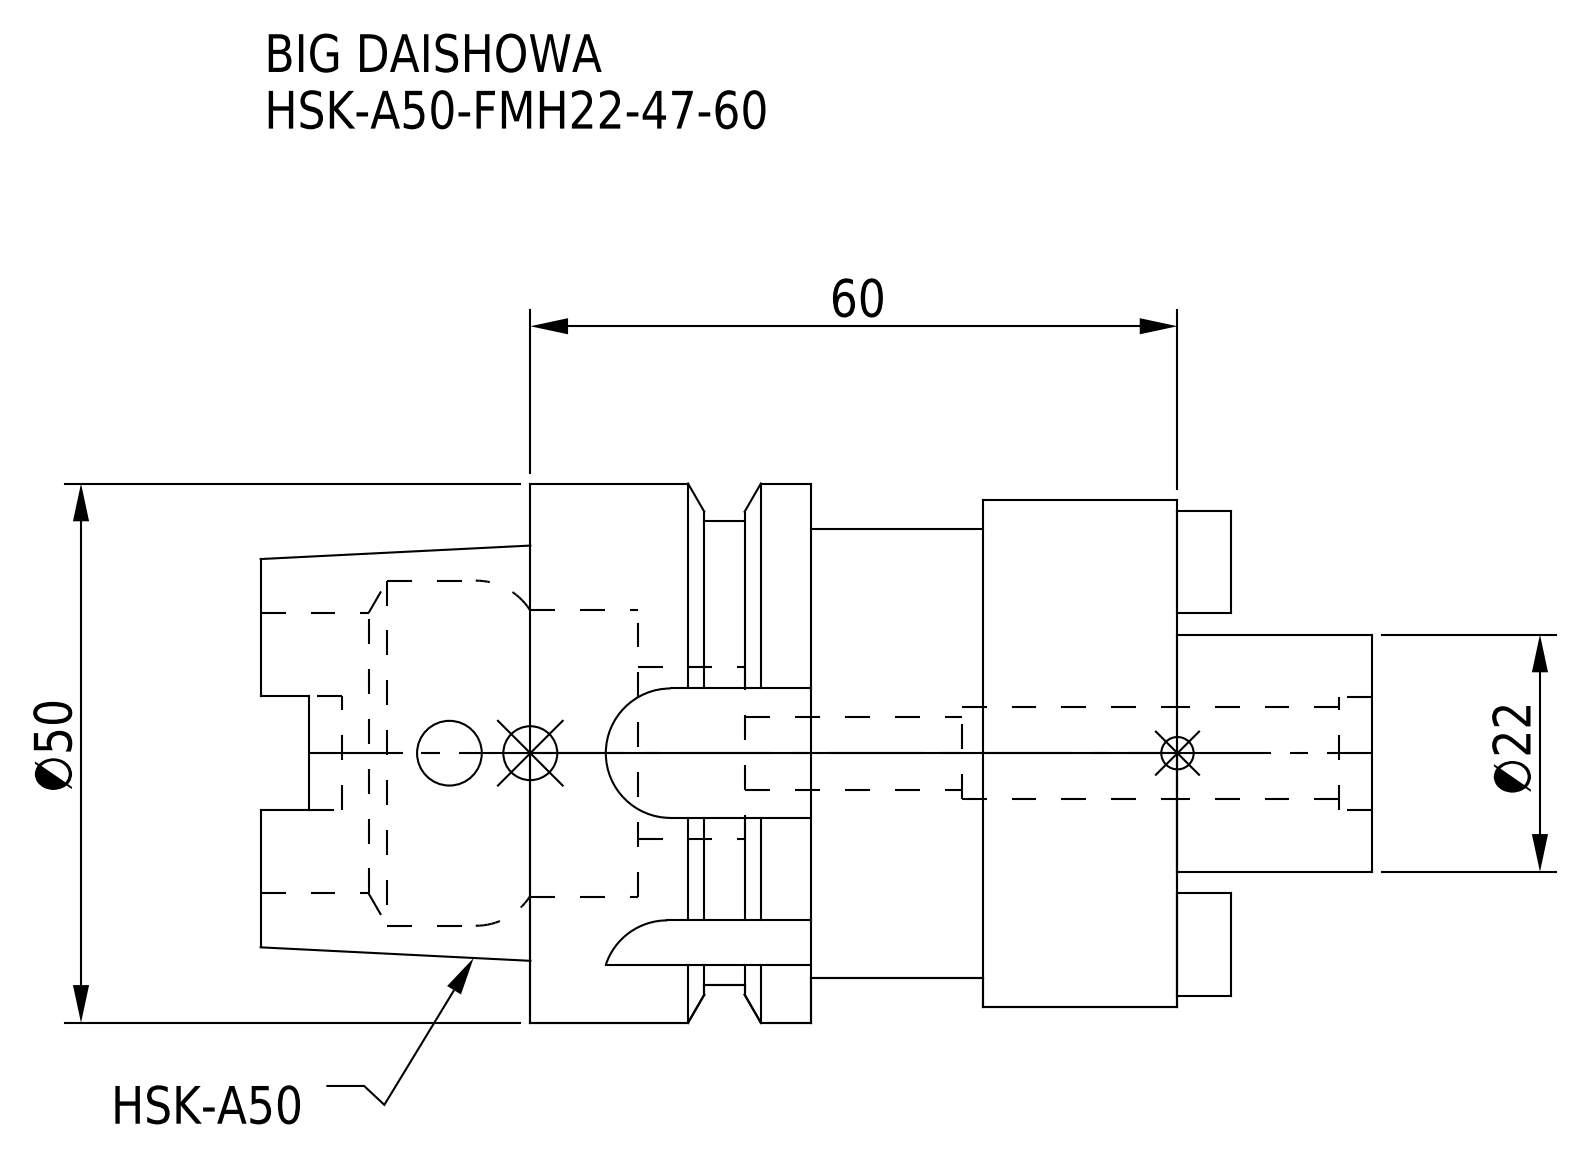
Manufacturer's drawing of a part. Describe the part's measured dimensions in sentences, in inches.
The part is named "HSK-A50-FMH22-47-60". Its 3-D file was written by "CREO PARAMETRIC BY PTC INC, 2016380 (AUTOMOTIVE_DESIGN)". It is 1 solid with 107 faces: 50 planar, 43 cylindrical and 14 other. Overall it measures 4.055 by 1.969 by 1.969 inches. Its volume is 6.531 cubic inches and its surface area 36.59 square inches. Round holes: 1 of diameter 0.236, 1 of diameter 0.268, 1 of diameter 0.335, 1 of diameter 0.413, 1 of diameter 0.63, 1 of diameter 1.024, 1 of diameter 1.047, 1 of diameter 1.26. Round bosses or shafts: 1 of diameter 1.969, 1 of diameter 1.85, 1 of diameter 1.693, 1 of diameter 1.638, 1 of diameter 0.866. Partial cylindrical surfaces (rounded edges, fillets, slot ends): 4 of radius 0.094, 4 of radius 0.236. The main face-to-face distances are 2.362, 1.024, 0.709, 1.654, 0.63, 1.339, 1.97, 1.262, 0.632, 0.392.
